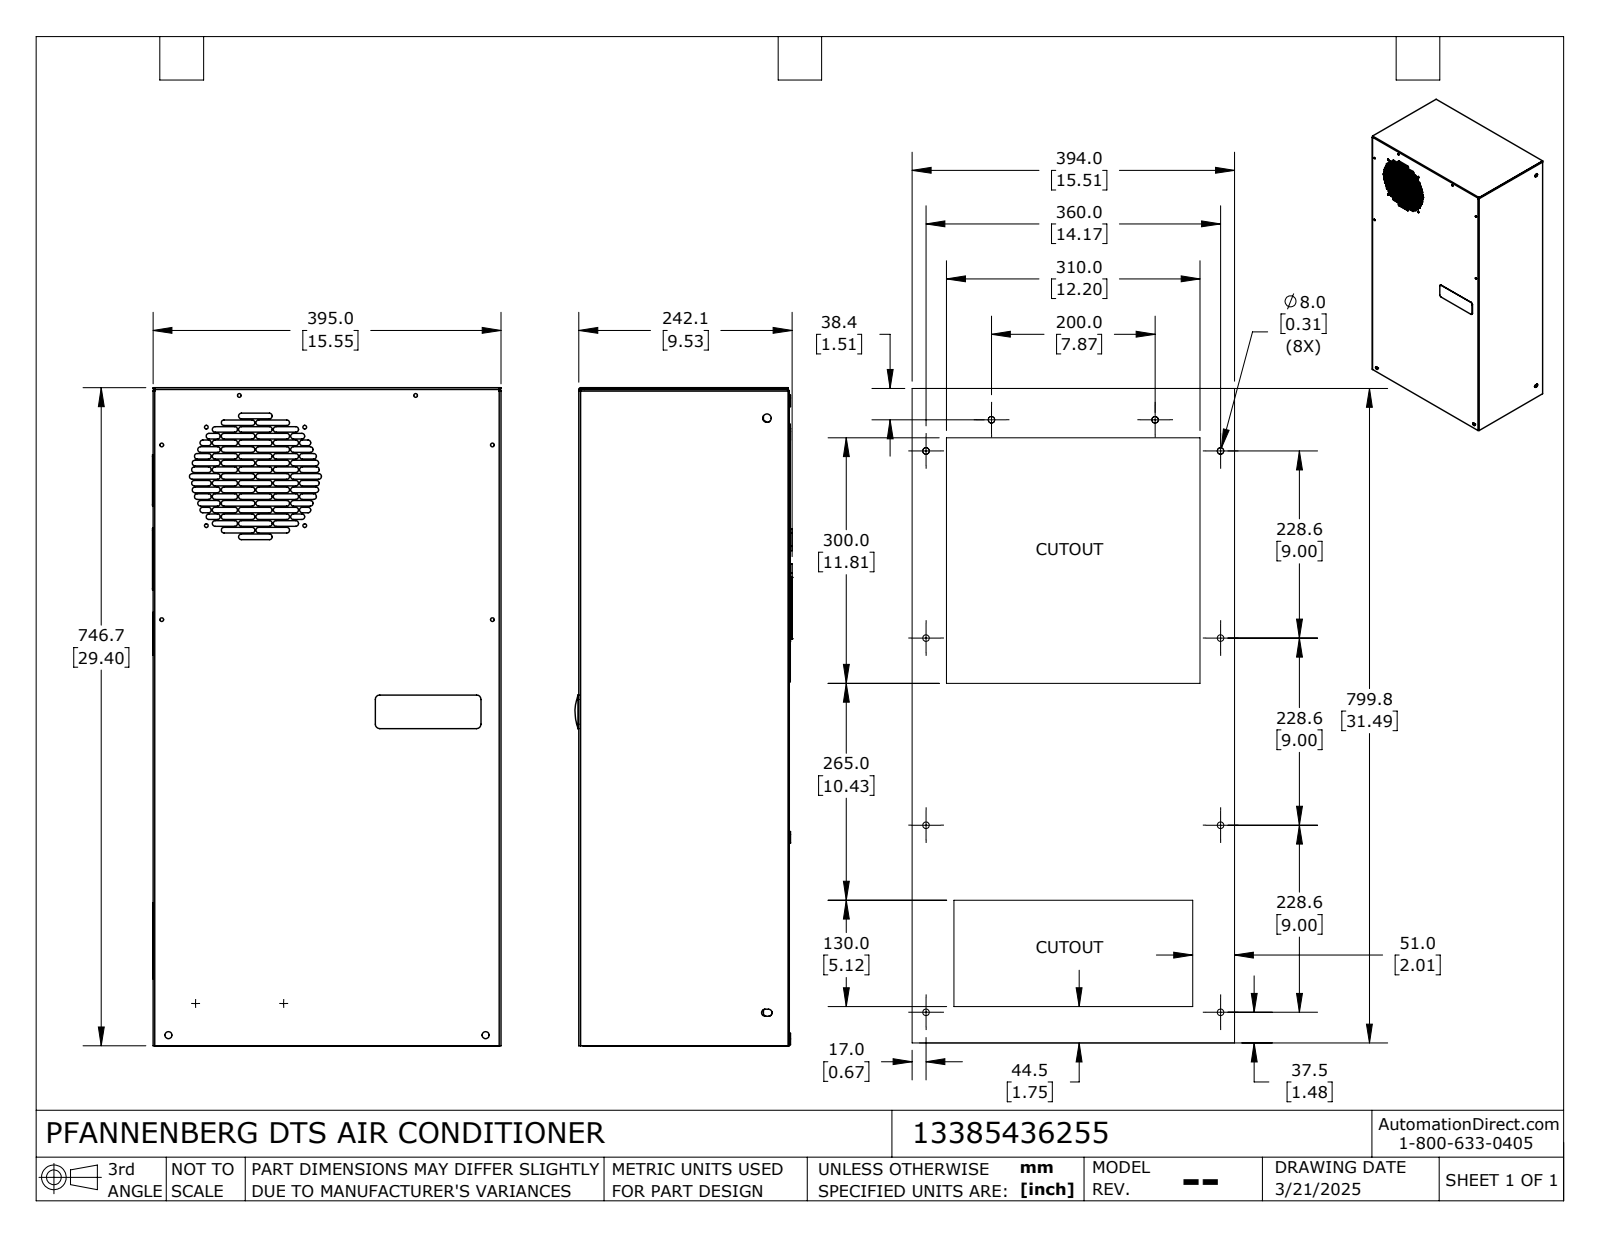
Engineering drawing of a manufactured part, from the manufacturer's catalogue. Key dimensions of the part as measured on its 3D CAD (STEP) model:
Part name (STEP PRODUCT): 13385436255_Default
STEP written by: SolidWorks 2024 (CONFIG_CONTROL_DESIGN)
Units: inches
Bodies: 1 solid, 1943 faces (1110 planar, 805 cylindrical, 28 other)
Overall size (bounding box): 29.397 × 15.571 × 9.704
Volume: 4 068 in³ · Surface area: 5 117 in²
Round holes (diameter × count): ⌀0.165 ×20, ⌀0.161 ×12, ⌀0.283 ×10, ⌀0.157 ×6, ⌀0.197 ×4, ⌀0.315 ×2, ⌀0.437 ×2, ⌀0.318 ×1, ⌀0.375 ×1, ⌀0.825 ×1, ⌀1 ×1, ⌀1.25 ×1
Round bosses / shafts (diameter × count): ⌀0.512 ×10
Partial cylindrical surfaces — rounded edges, fillets, slot ends (radius × count): R0.125 ×140, R0.112 ×130, R0.031 ×18, R0.079 ×18, R0.085 ×16, R0.079 ×12, R0.197 ×12, R0.113 ×10
Main face-to-face distances: 0.048, 15.504, 0.036, 9.026, 9.243, 0.217, 9.29, 0.264, 0.115, 9.141
Hole centre spacings: 4.398, 0.172, 0.243, 4.669, 6.22, 7.802, 7.874, 9.012
